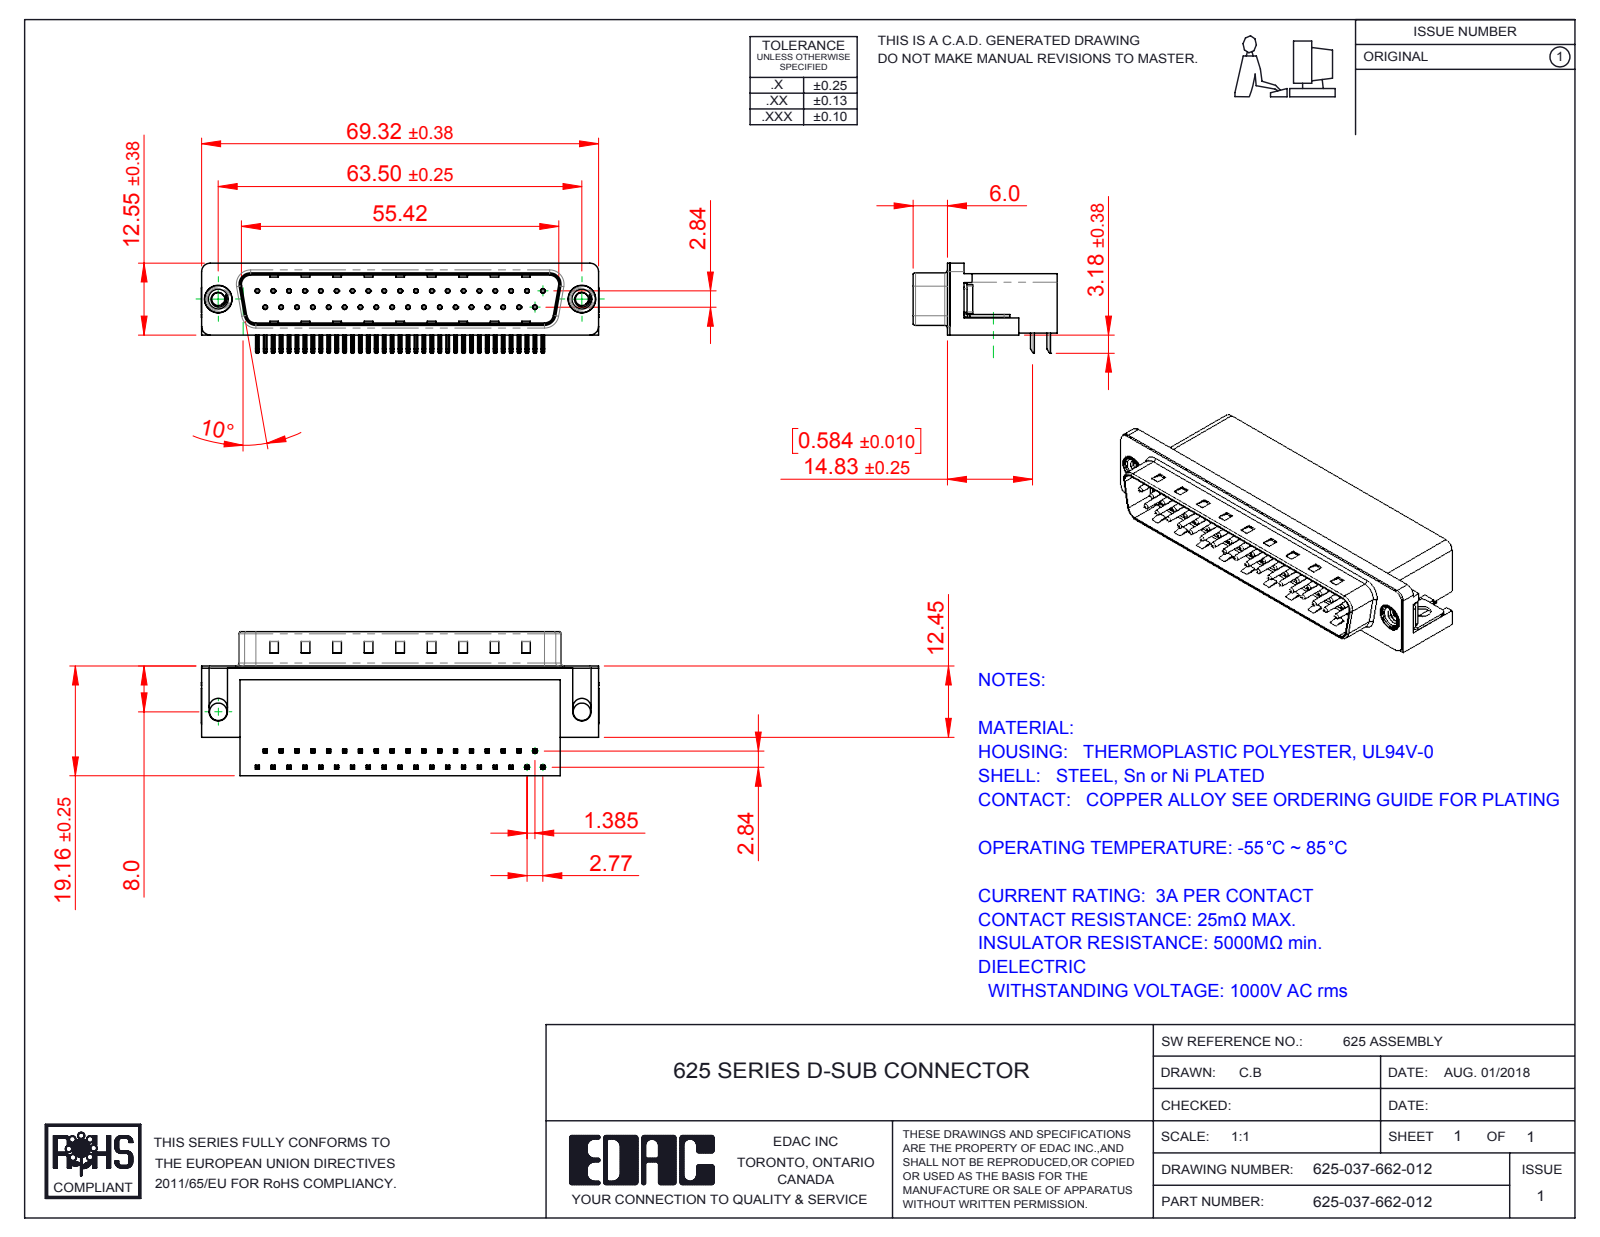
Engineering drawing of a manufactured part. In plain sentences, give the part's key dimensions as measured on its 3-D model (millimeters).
The part is named "625 4-40 Threaded Rivet; 625 Thru Hole Board Mount; 625-037-662-012; 625 Shell_37 Socket (+3 more)". Its 3-D file was written by "SolidWorks 2016 (CONFIG_CONTROL_DESIGN)". It is 43 solids with 3201 faces: 2013 planar, 917 cylindrical and 271 other. Overall it measures 69.4 by 25.16 by 15.73 millimeters. Its volume is 12 599 cubic millimeters and its surface area 11 741 square millimeters. Round holes: 37 of diameter 0.35, 37 of diameter 0.8, 2 of diameter 2.26, 2 of diameter 3.05, 2 of diameter 4, 2 of diameter 4.8, 2 of diameter 5. Round bosses or shafts: 37 of diameter 0.75, 2 of diameter 4.9, 2 of diameter 4.75, 2 of diameter 3.9. Partial cylindrical surfaces (rounded edges, fillets, slot ends): 156 of radius 0.25, 74 of radius 0.12, 16 of radius 1, 9 of radius 0.5, 8 of radius 1.6, 7 of radius 1.5, 4 of radius 0.9, 4 of radius 2. The main face-to-face distances are 10.34, 0.4, 18.76, 8.76, 19.16, 2.84, 2.09, 10.1, 1.74, 8.36. The hole center spacings are 3.16, 2.77, 5.54, 8.31, 11.08, 13.85, 19.39, 22.16.
